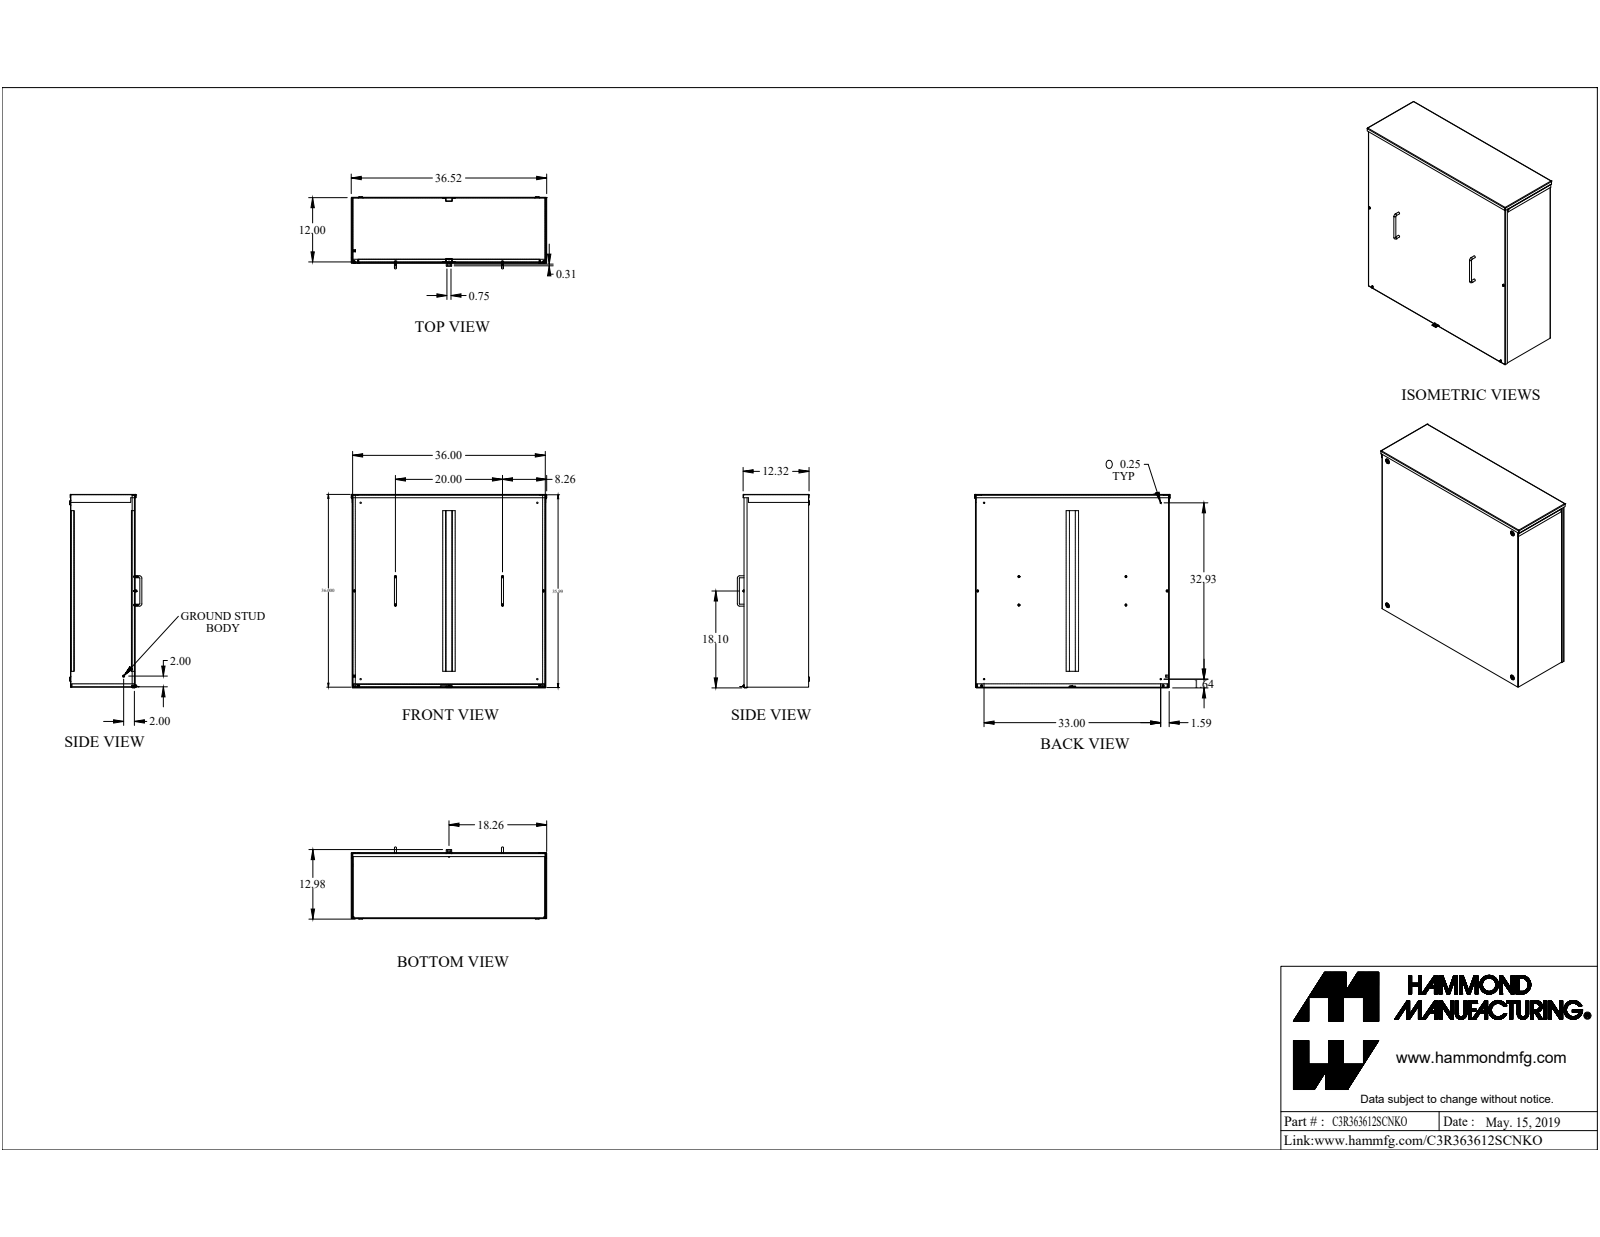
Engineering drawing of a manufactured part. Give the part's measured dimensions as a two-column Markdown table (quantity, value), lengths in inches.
| quantity | value |
| --- | --- |
| part name | C3R363612SCNKO |
| STEP written by | SolidWorks 2019 (AUTOMOTIVE_DESIGN) |
| units | inches |
| bodies | 19 solids, 497 faces (315 planar, 122 cylindrical, 60 other) |
| overall size | 36.519 × 36.135 × 13.478 |
| volume | 346.5 in³ |
| surface area | 9 551 in² |
| round holes (diameter × count) | 0.156 × 5, 0.17 × 4, 0.203 × 4, 0.25 × 4, 0.125 × 1, 0.137 × 1 |
| round bosses / shafts (diameter × count) | 0.375 × 9, 0.19 × 8, 0.367 × 4, 0.375 × 2, 0.125 × 1 |
| partial cylindrical surfaces (radius × count) | 0.036 × 28, 0.108 × 28, 0.109 × 8, 0.125 × 8, 0.156 × 2, 0.029 × 1, 0.086 × 1 |
| main face-to-face distances | 0.072, 12, 11.928, 12.072, 35.928, 36, 0.072, 35.856, 35.856, 35.928 |
| hole center spacings | 20, 0.024, 5.3, 8.139, 15.267, 16.507, 20.189, 20.69 |
